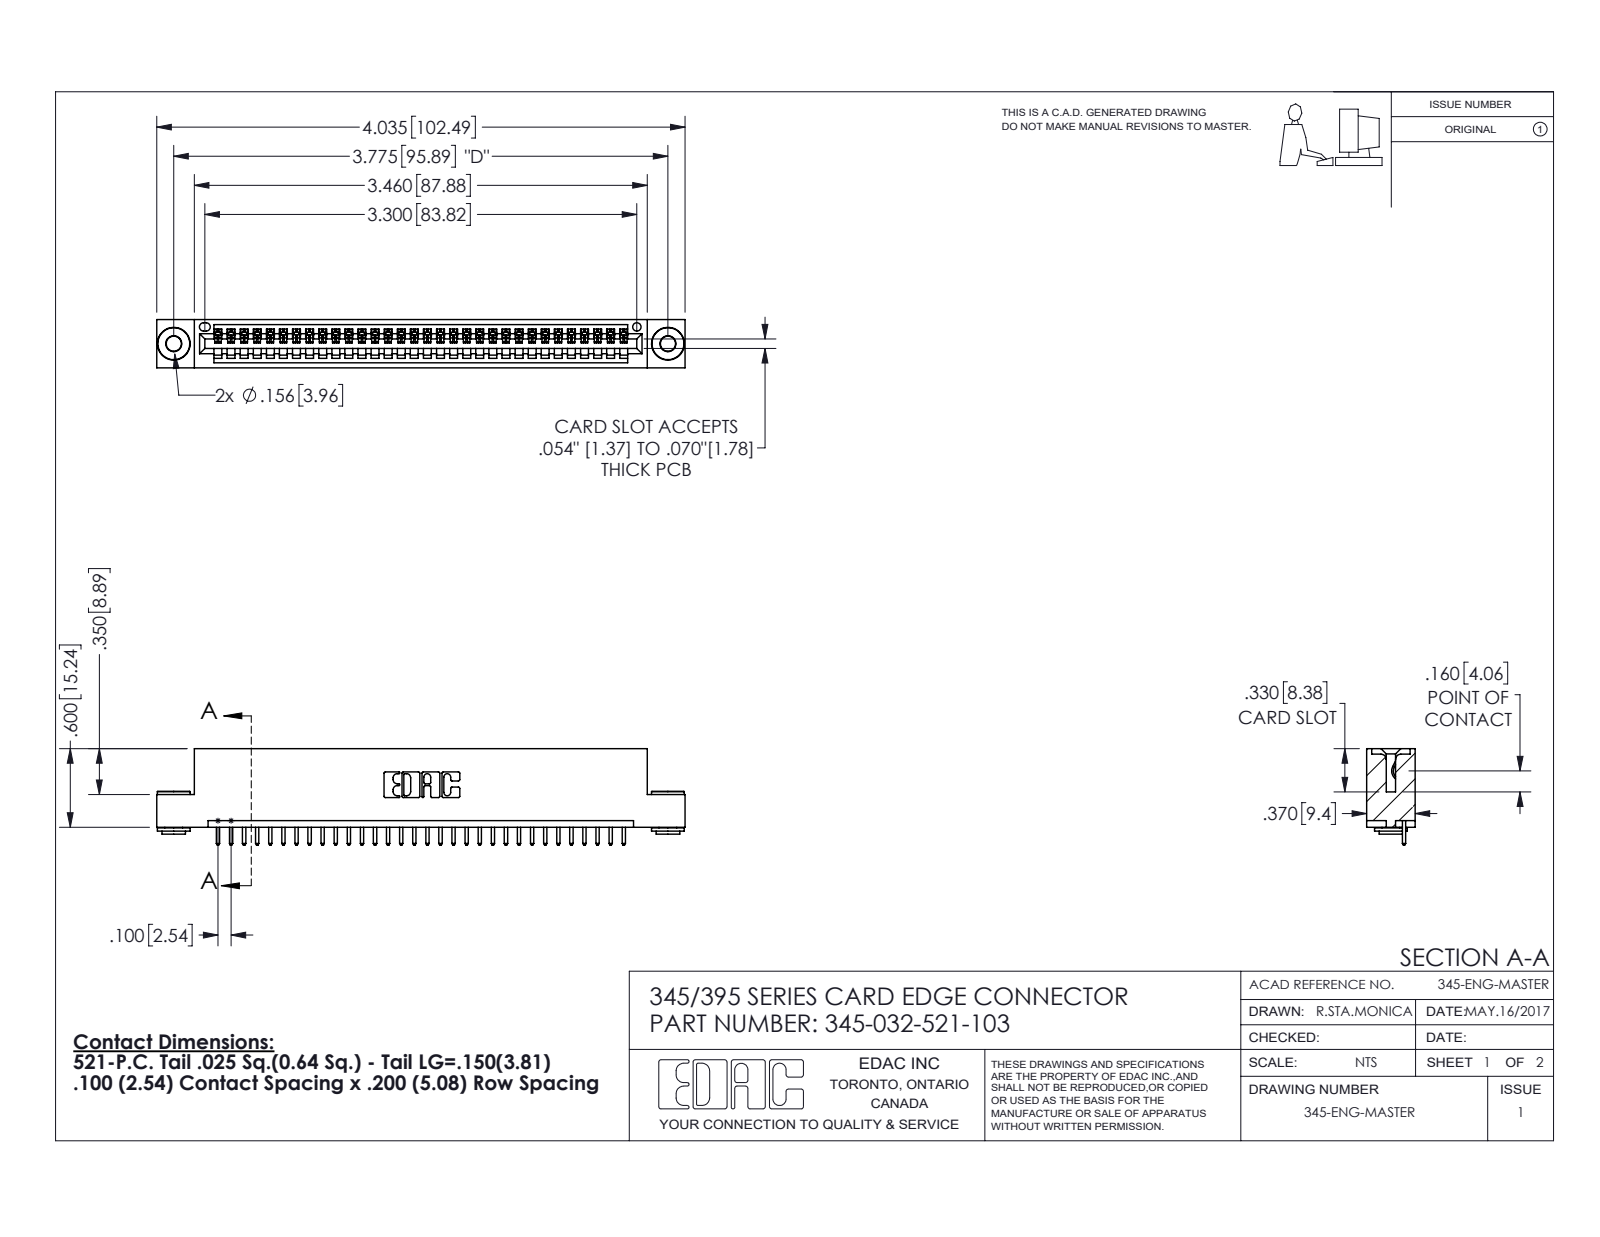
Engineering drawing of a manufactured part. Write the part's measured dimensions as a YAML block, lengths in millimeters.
part_name: "345-292-001_345-293-121; 345-250-002_345-250-002-102; 345-032-521-103; 345 Part_Flush Mounting Lugs - 0.156 Dia-TH"
step_written_by: "SolidWorks 2016 (CONFIG_CONTROL_DESIGN)"
units: millimeters
bodies: {solids: 35, faces: 2020, planar: 1370, cylindrical: 642, other: 8}
overall_size: [102.5, 18.7, 9.4]
volume: 9590
surface_area: 12450
round_holes:
  - {diameter: 2.9, count: 2}
  - {diameter: 4, count: 2}
  - {diameter: 1.6, count: 1}
round_bosses_or_shafts:
  - {diameter: 6.4, count: 2}
  - {diameter: 4.6, count: 2}
  - {diameter: 3.5, count: 2}
partial_cylinders:
  - {radius: 0.2, count: 64}
  - {radius: 0.3, count: 64}
  - {radius: 0.3, count: 22}
  - {radius: 0.2, count: 6}
  - {radius: 0.8, count: 6}
  - {radius: 0.7, count: 3}
  - {radius: 0.8, count: 2}
  - {radius: 1, count: 2}
face_to_face_distances: [1.8, 7.6, 5.1, 9.4, 0.6, 2.5, 6.9, 5.7, 3.8, 1.8]
hole_center_spacings: [6.9, 89.9, 95.9]
